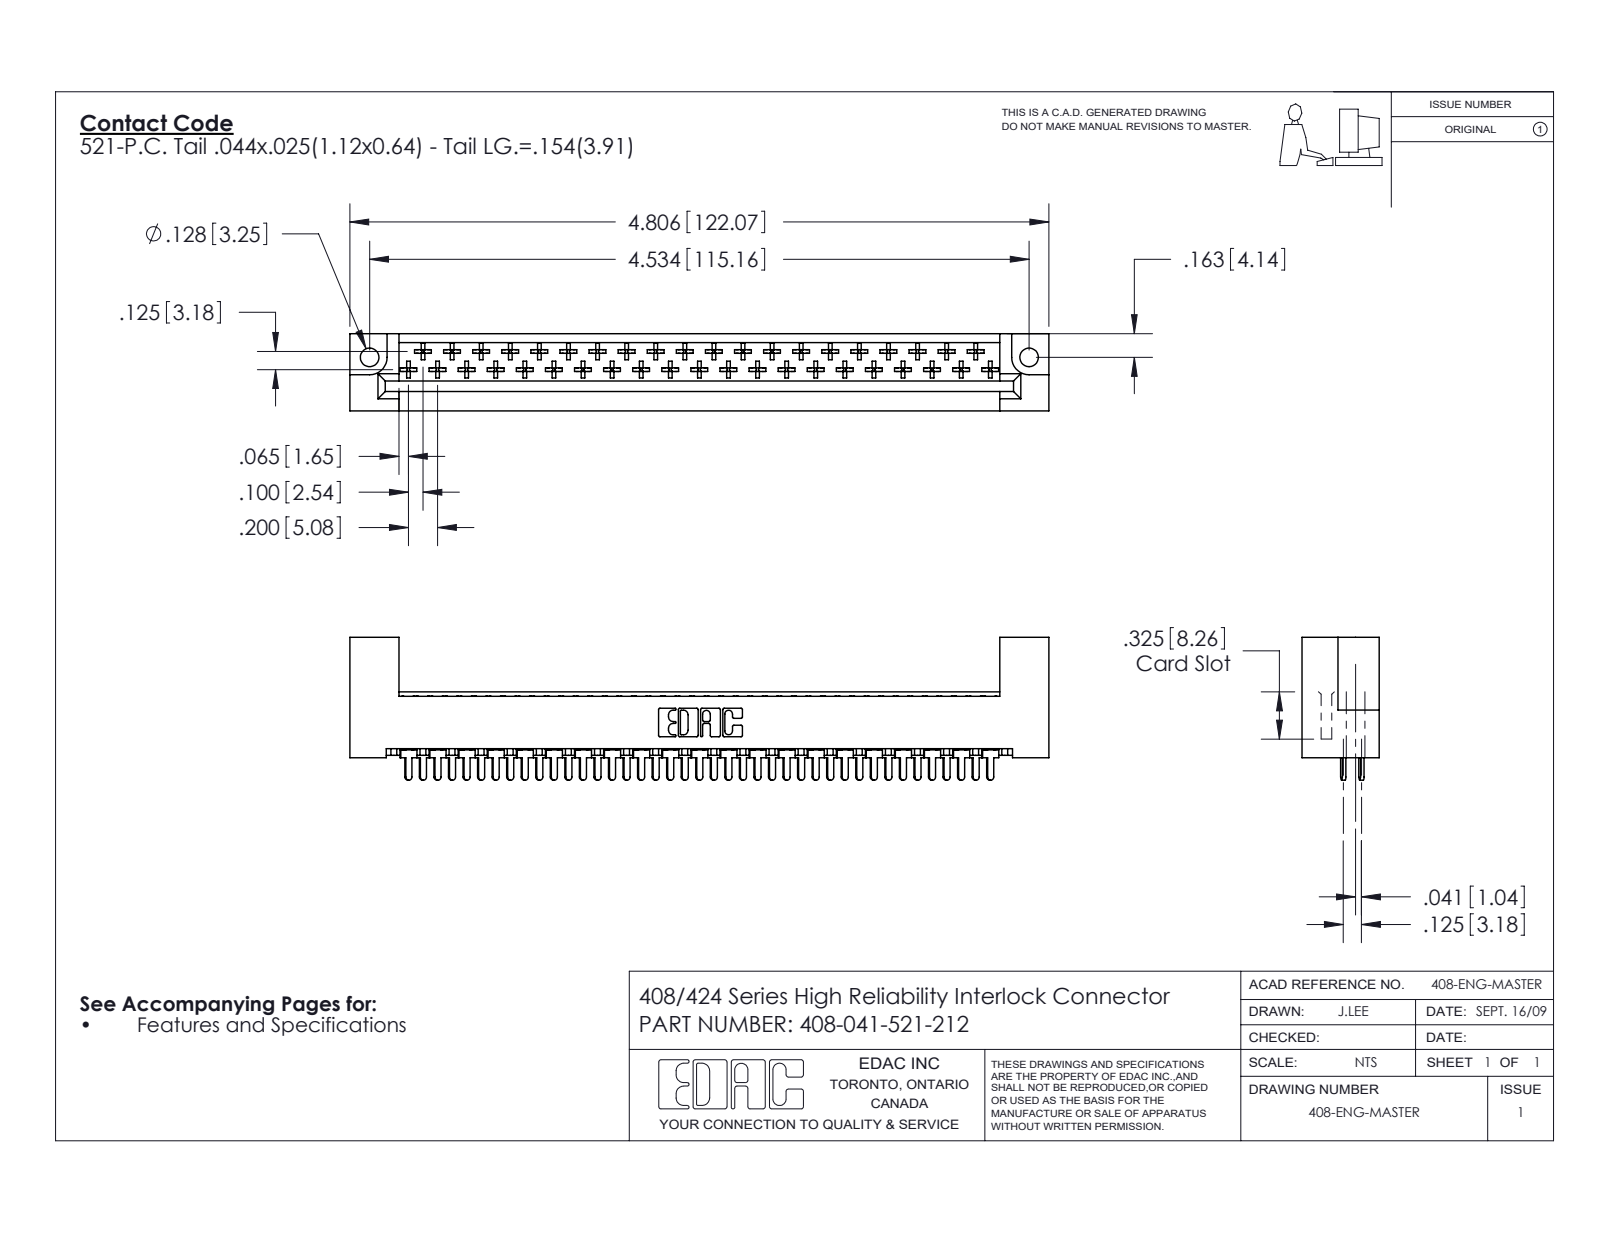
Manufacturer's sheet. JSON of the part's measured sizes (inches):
{"part_name": "408-047-521-212; 408-290-001_408-290-121; 408 Part_041 - 2", "step_written_by": "SolidWorks 2016 (CONFIG_CONTROL_DESIGN)", "units": "inches", "bodies": {"solids": 42, "faces": 2394, "planar": 1811, "cylindrical": 419, "other": 164}, "overall_size": [4.806, 0.982, 0.531], "volume_in3": 0.917, "surface_area_in2": 27.31, "round_holes": [[0.128, 2]], "partial_cylinders_radius": [[0.01, 246], [0.02, 43], [0.022, 41], [0.01, 22], [0.007, 6], [0.031, 6], [0.026, 3], [0.12, 2]], "face_to_face_distances": [0.531, 0.125, 0.1, 0.025, 0.025, 0.361, 0.235, 0.259, 0.398, 0.217], "hole_center_spacings": [4.534]}
